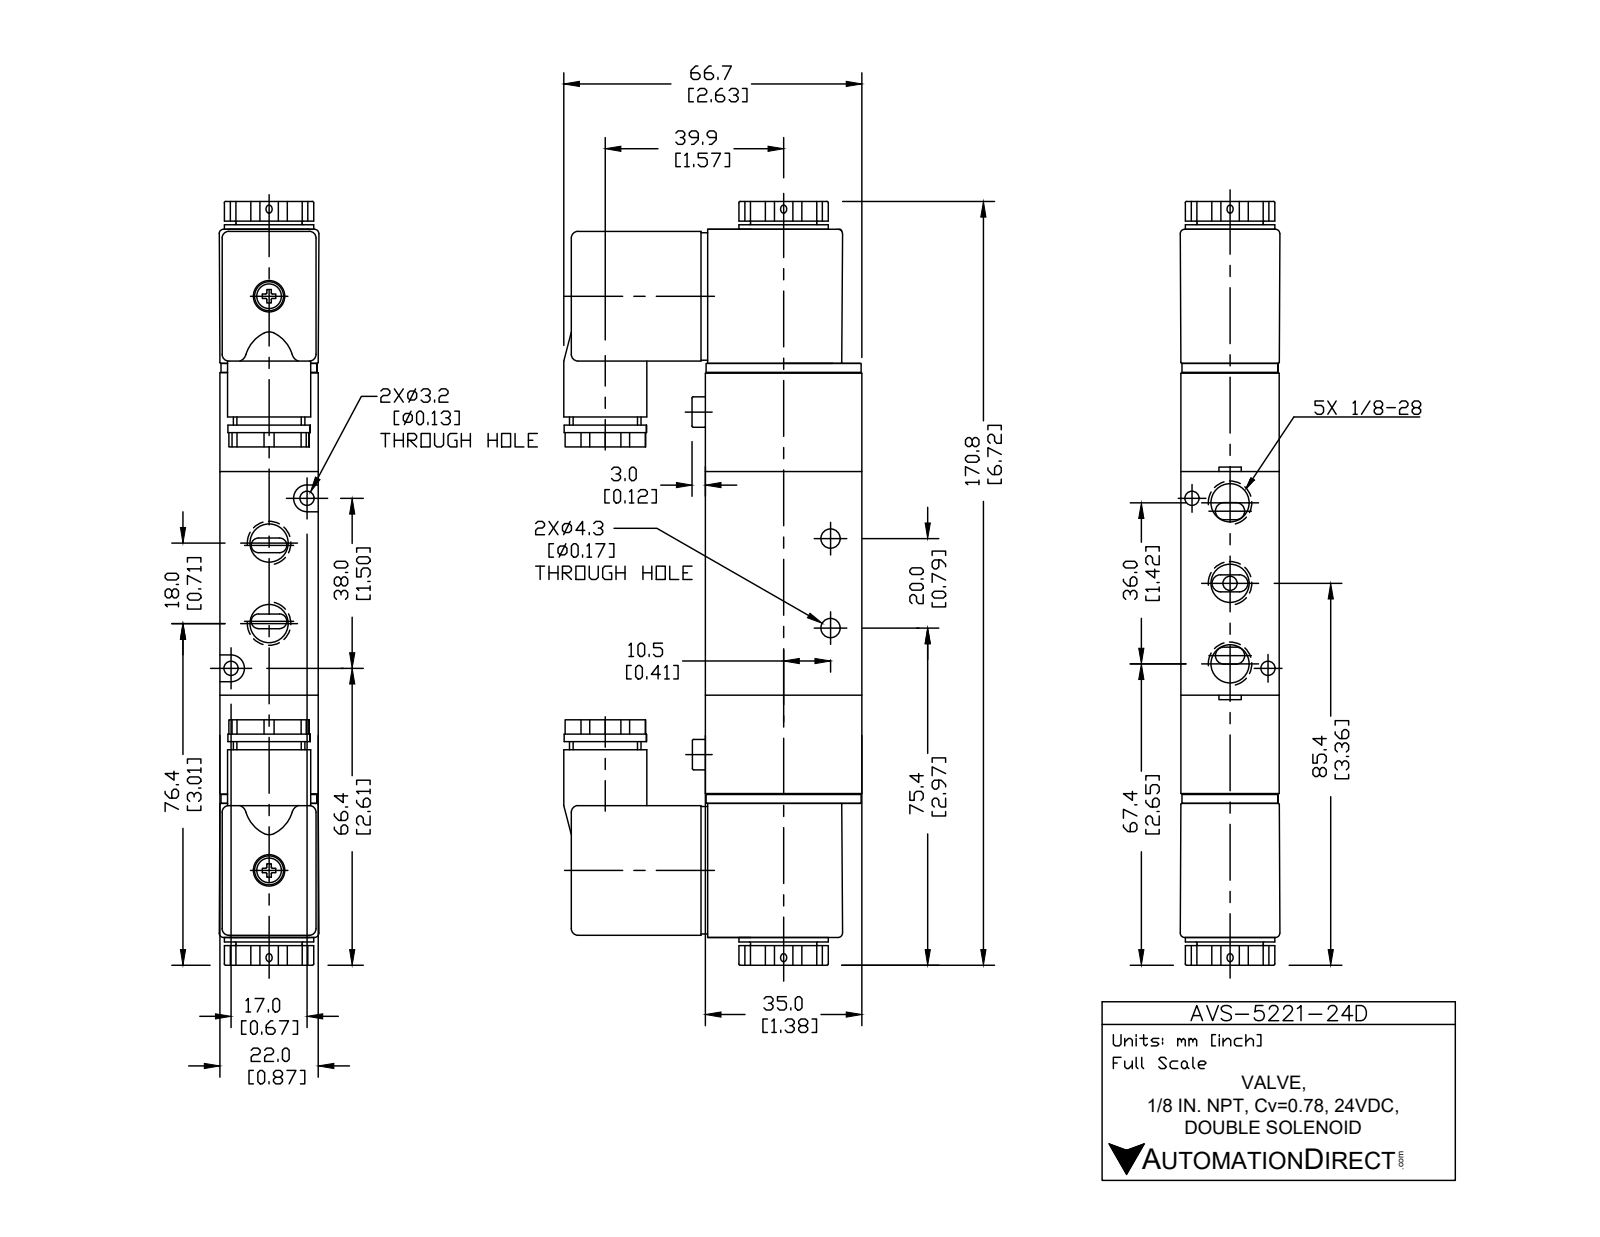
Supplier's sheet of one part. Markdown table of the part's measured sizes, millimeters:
| quantity | value |
| --- | --- |
| part name | AVS-5221-24D |
| STEP written by | SolidWorks 2015 (CONFIG_CONTROL_DESIGN) |
| units | millimeters |
| bodies | 5 solids, 278 faces (133 planar, 111 cylindrical, 34 other) |
| overall size | 170.8 × 66.7 × 22 |
| volume | 158 275 mm³ |
| surface area | 35 246 mm² |
| round holes (diameter × count) | 8.43 × 5, 4.3 × 2, 3.2 × 1, 3.3 × 1, 9.3 × 1 |
| round bosses / shafts (diameter × count) | 6.7 × 2, 20 × 1, 18.6 × 1, 18.4 × 1, 16 × 1, 14.8 × 1 |
| partial cylindrical surfaces (radius × count) | 1.5 × 18, 1 × 10, 1.54 × 10, 0.5 × 8, 3 × 2 |
| main face-to-face distances | 0.5, 22, 21.5, 35, 22.88, 21, 50, 30, 65, 53.7 |
| hole center spacings | 9, 18, 8.56, 13.12, 20.81, 27, 29.26, 37.96 |
